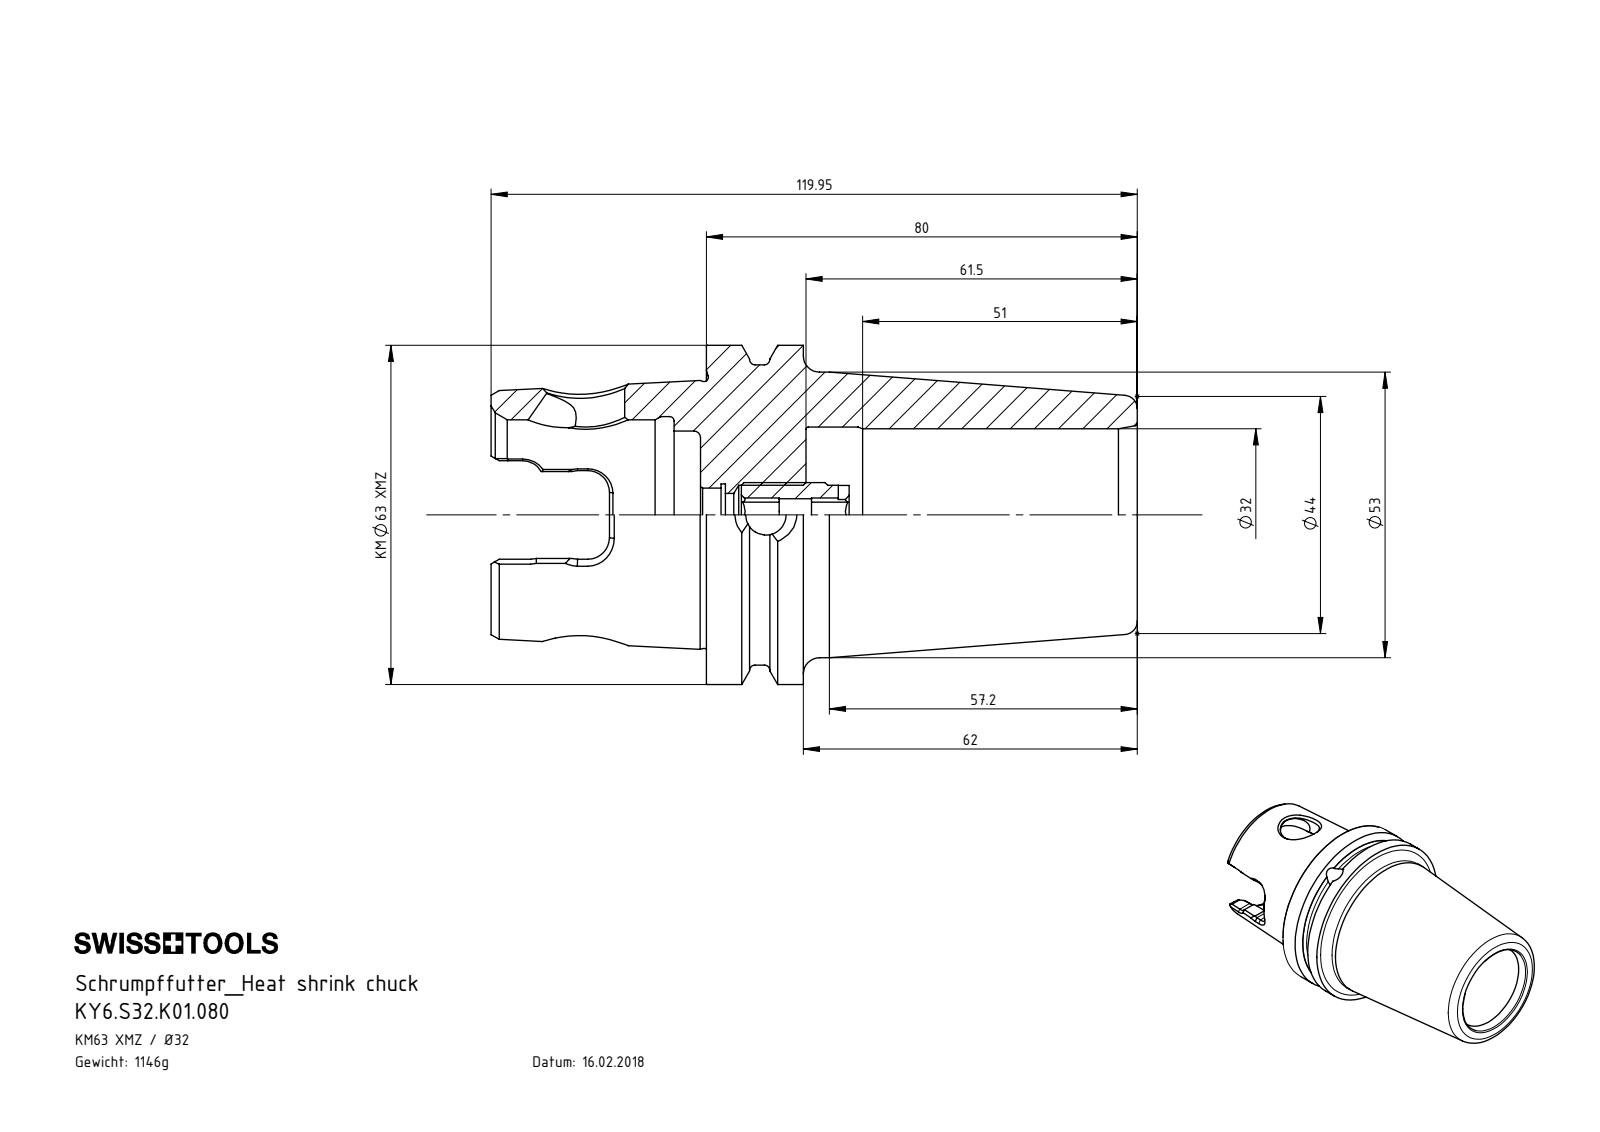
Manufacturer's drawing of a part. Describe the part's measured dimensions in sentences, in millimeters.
The part is named "KY6.S32.K01.080; KY6-S32.K01.080_A; ERU-AN5.K01.020_A". Its 3-D file was written by "SolidWorks 2017 (CONFIG_CONTROL_DESIGN)". It is 2 solids with 277 faces: 79 planar, 60 cylindrical and 138 other. Overall it measures 119.95 by 62.95 by 62.95 millimeters. Its volume is 145 997 cubic millimeters and its surface area 36 214 square millimeters. Round holes: 2 of diameter 7.47, 1 of diameter 6, 1 of diameter 8, 1 of diameter 8.48, 1 of diameter 10, 1 of diameter 11, 1 of diameter 11.5, 1 of diameter 14.5, 1 of diameter 31.1, 1 of diameter 32, 1 of diameter 32.6, 1 of diameter 35.27. Round bosses or shafts: 1 of diameter 62.95, 1 of diameter 55.7, 1 of diameter 53, 1 of diameter 12. Partial cylindrical surfaces (rounded edges, fillets, slot ends): 6 of radius 4, 2 of radius 7.04. The main face-to-face distances are 18.5, 1.1, 19.6, 18, 19.1, 0.5, 6, 81.1, 80, 62.
